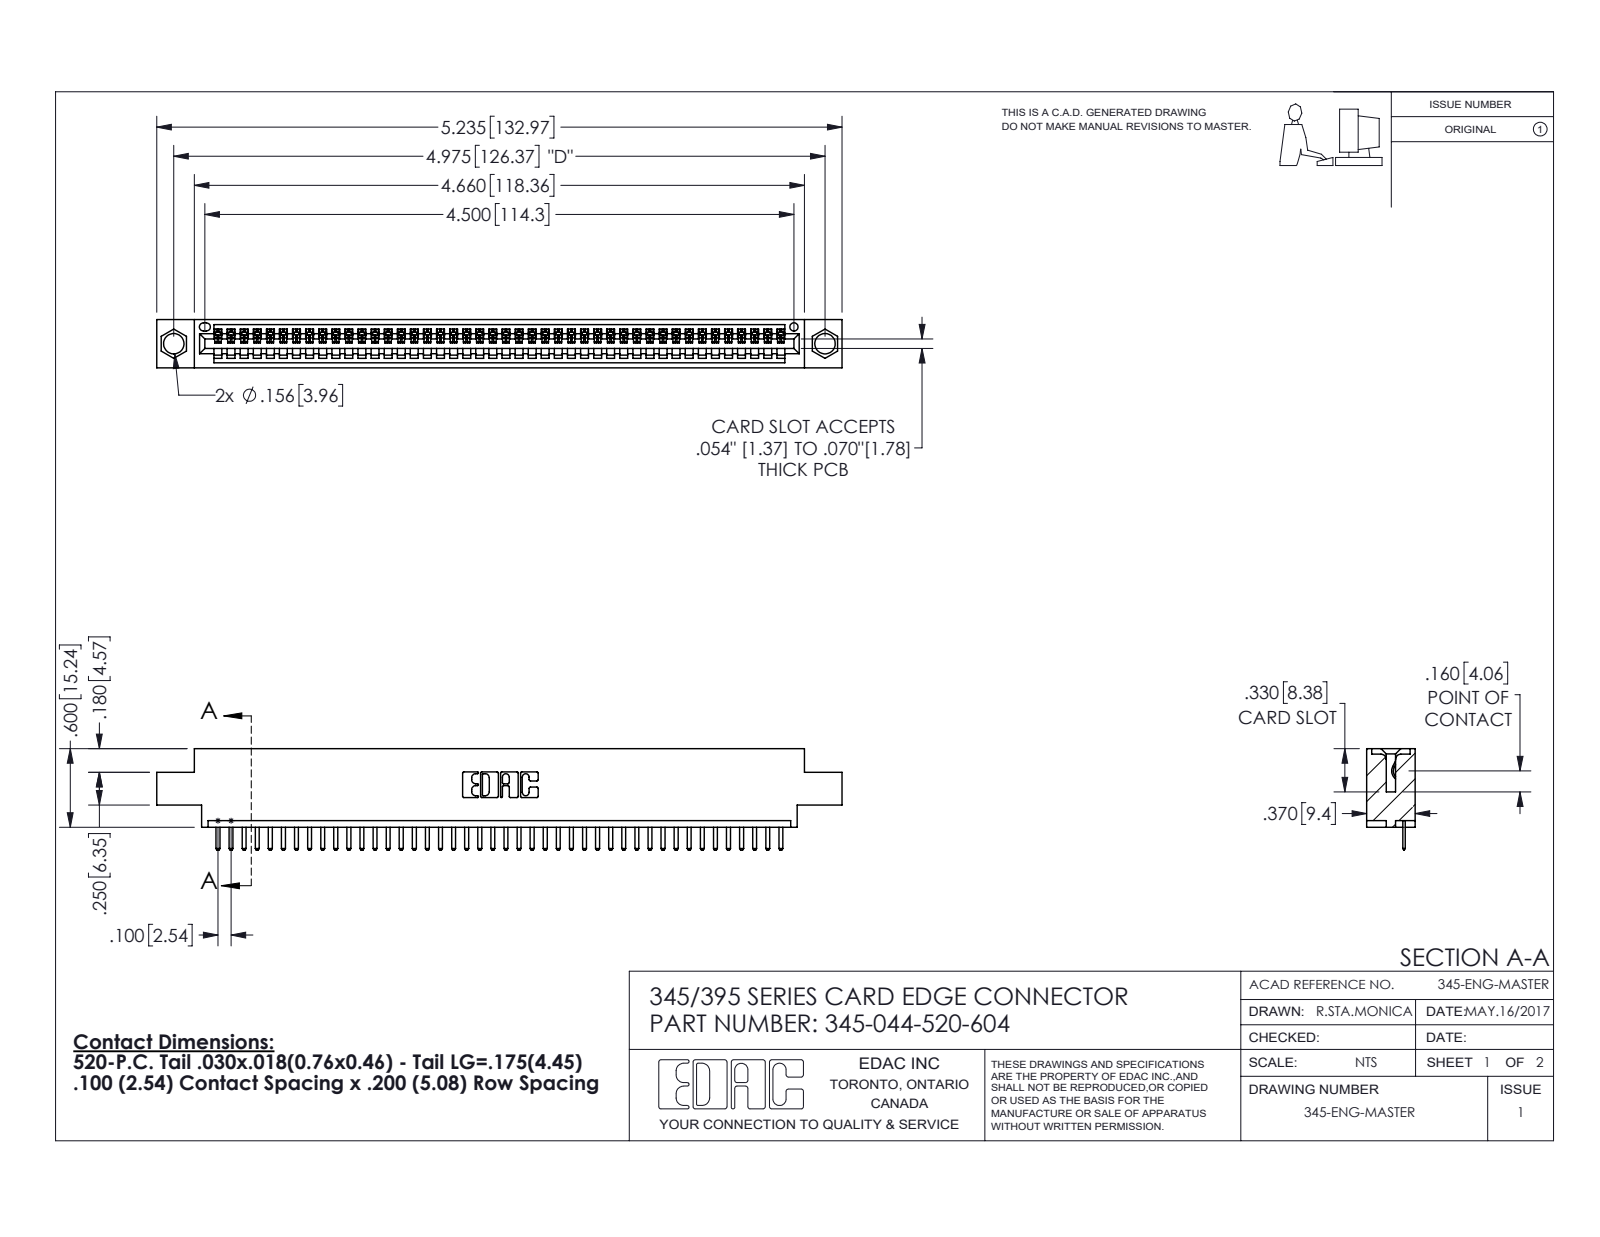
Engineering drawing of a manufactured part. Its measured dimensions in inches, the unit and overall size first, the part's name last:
Units: inches
Overall size (bounding box): 5.235 × 0.775 × 0.37
Round holes (diameter × count): ⌀0.156 ×2, ⌀0.064 ×1
Partial cylindrical surfaces — rounded edges, fillets, slot ends (radius × count): R0.01 ×90, R0.006 ×88, R0.01 ×22, R0.007 ×6, R0.031 ×6, R0.026 ×3, R0.031 ×2, R0.04 ×2
Main face-to-face distances: 0.072, 0.298, 0.37, 0.2, 0.098, 0.272, 0.025, 0.225, 0.072, 0.175
Hole centre spacings: 0.27, 4.739, 4.975
Volume: 0.752 in³ · Surface area: 24.67 in²
Bodies: 45 solids, 2858 faces (1932 planar, 926 cylindrical, 0 other)
Part name (STEP PRODUCT): 345-044-520-604; 345-292-001_345-293-120; 345 Part_0.170 Offset - 0.156 Dia-TH
STEP written by: SolidWorks 2016 (CONFIG_CONTROL_DESIGN)
